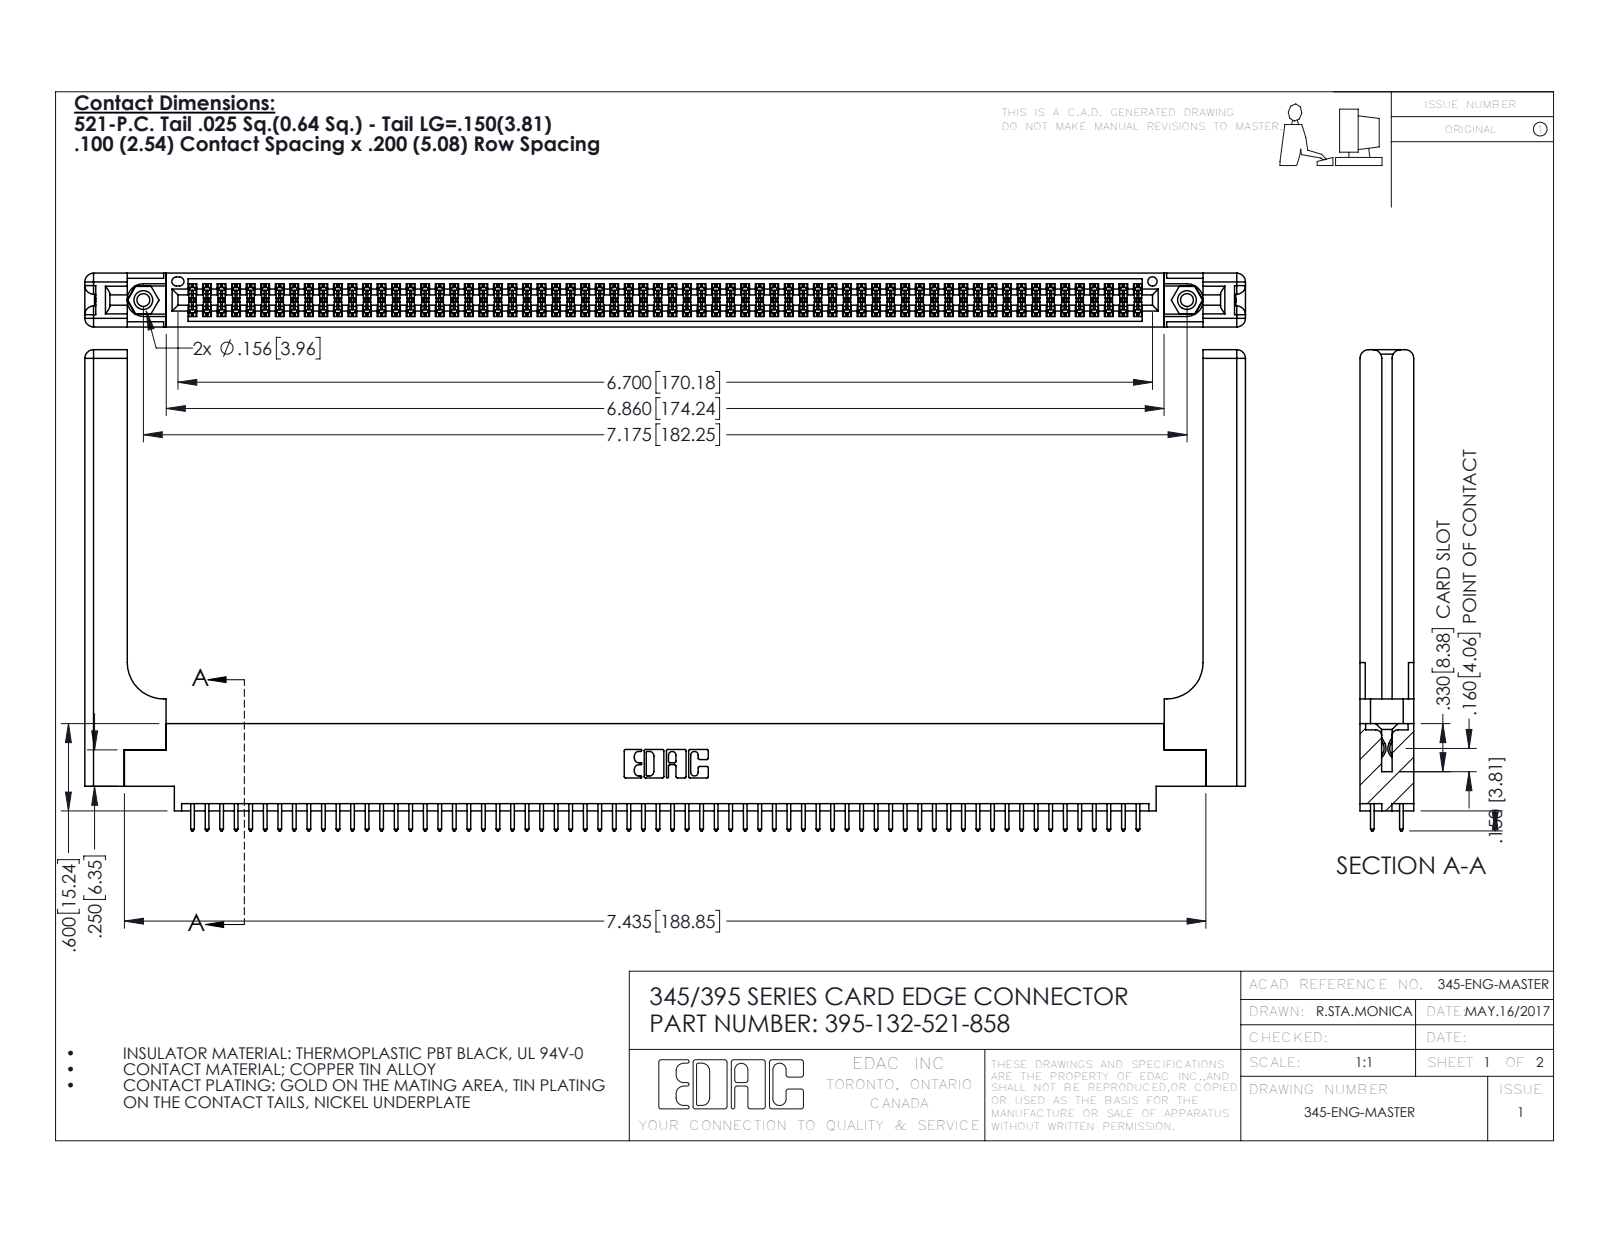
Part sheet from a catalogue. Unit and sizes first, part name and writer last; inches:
Units: inches
Overall size (bounding box): 7.979 × 3.307 × 0.37
Round holes (diameter × count): ⌀0.089 ×2, ⌀0.125 ×2, ⌀0.156 ×2, ⌀0.064 ×1
Round bosses / shafts (diameter × count): ⌀0.155 ×2
Partial cylindrical surfaces — rounded edges, fillets, slot ends (radius × count): R0.006 ×198, R0.01 ×132, R0.01 ×22, R0.06 ×16, R0.007 ×6, R0.031 ×6, R0.026 ×3, R0.014 ×2
Main face-to-face distances: 0.072, 0.298, 0.37, 0.098, 0.272, 0.025, 0.2, 0.225, 0.175, 0.148
Hole centre spacings: 0.27, 6.939, 7.175
Volume: 1.722 in³ · Surface area: 53.47 in²
Bodies: 137 solids, 6986 faces (4588 planar, 2338 cylindrical, 60 other)
Part name (STEP PRODUCT): 345-250-001_345-250-001-102; 395-132-521-858; 345 Part_0.170 Offset - 0.156 Dia-TH; 345-292-001_345-293-121 (+1 more)
STEP written by: SolidWorks 2016 (CONFIG_CONTROL_DESIGN)
